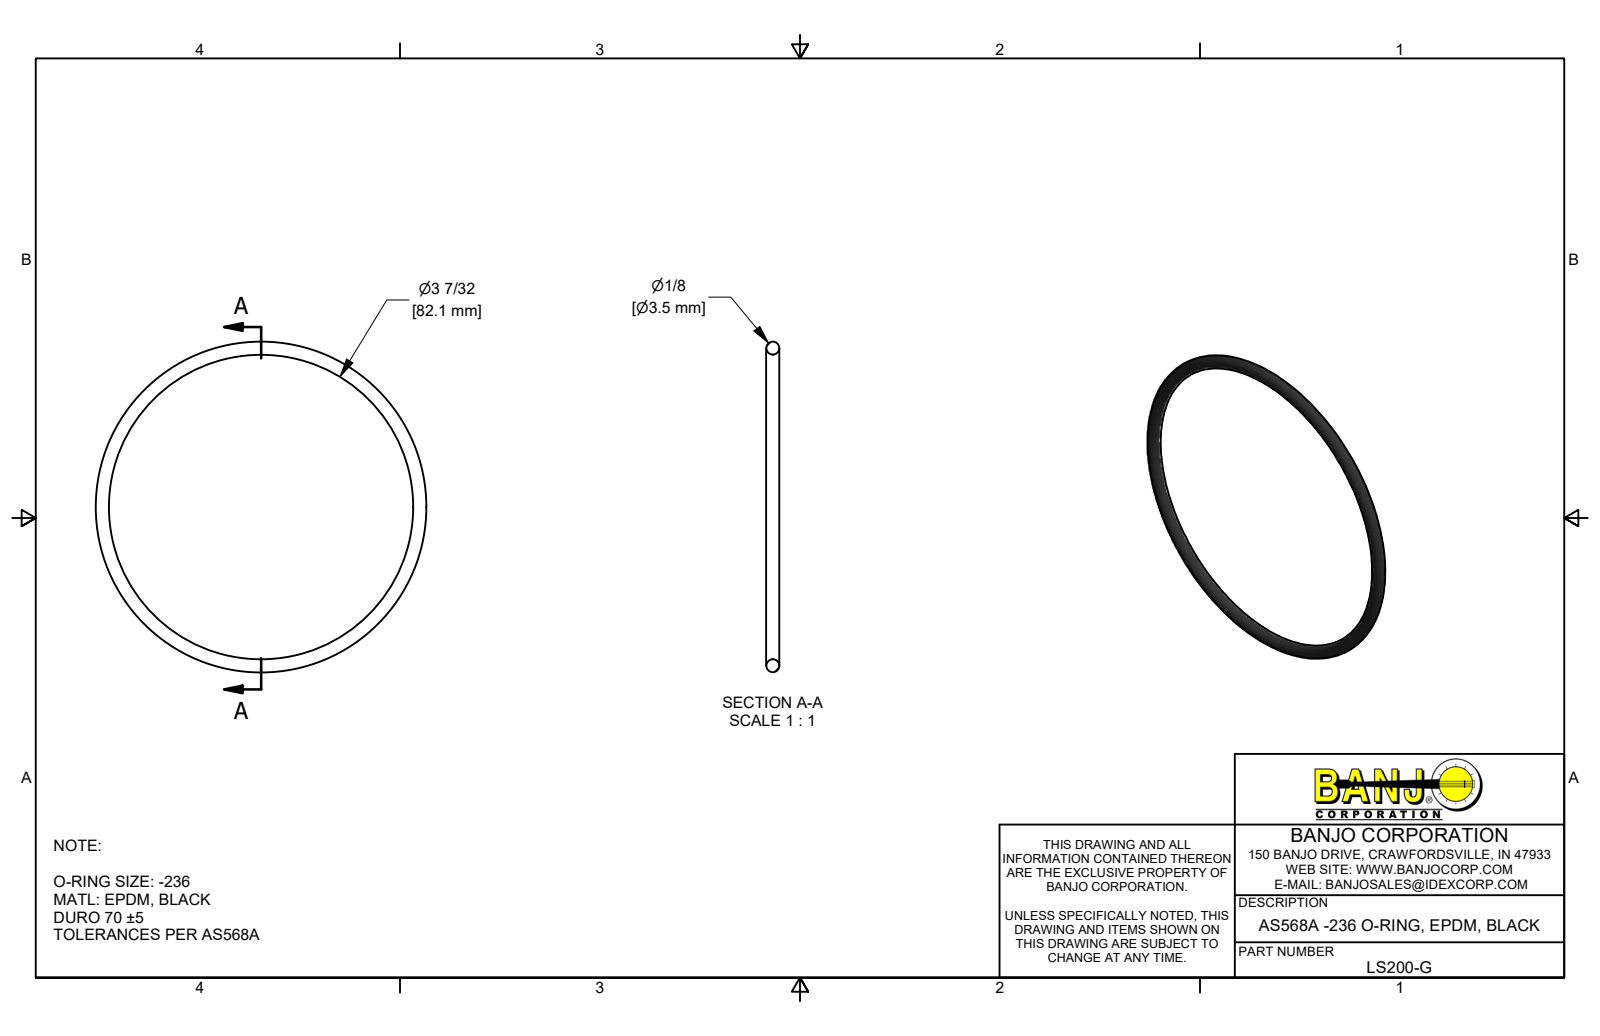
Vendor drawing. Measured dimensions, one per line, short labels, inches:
name: LS200-G
written by: Autodesk Inventor 2019 (AUTOMOTIVE_DESIGN)
unit: in
bodies: 1 solid, 1 faces (0 planar, 0 cylindrical, 1 other)
size: 3.512 × 3.512 × 0.139
volume: 0.161 in³; area: 4.627 in²
